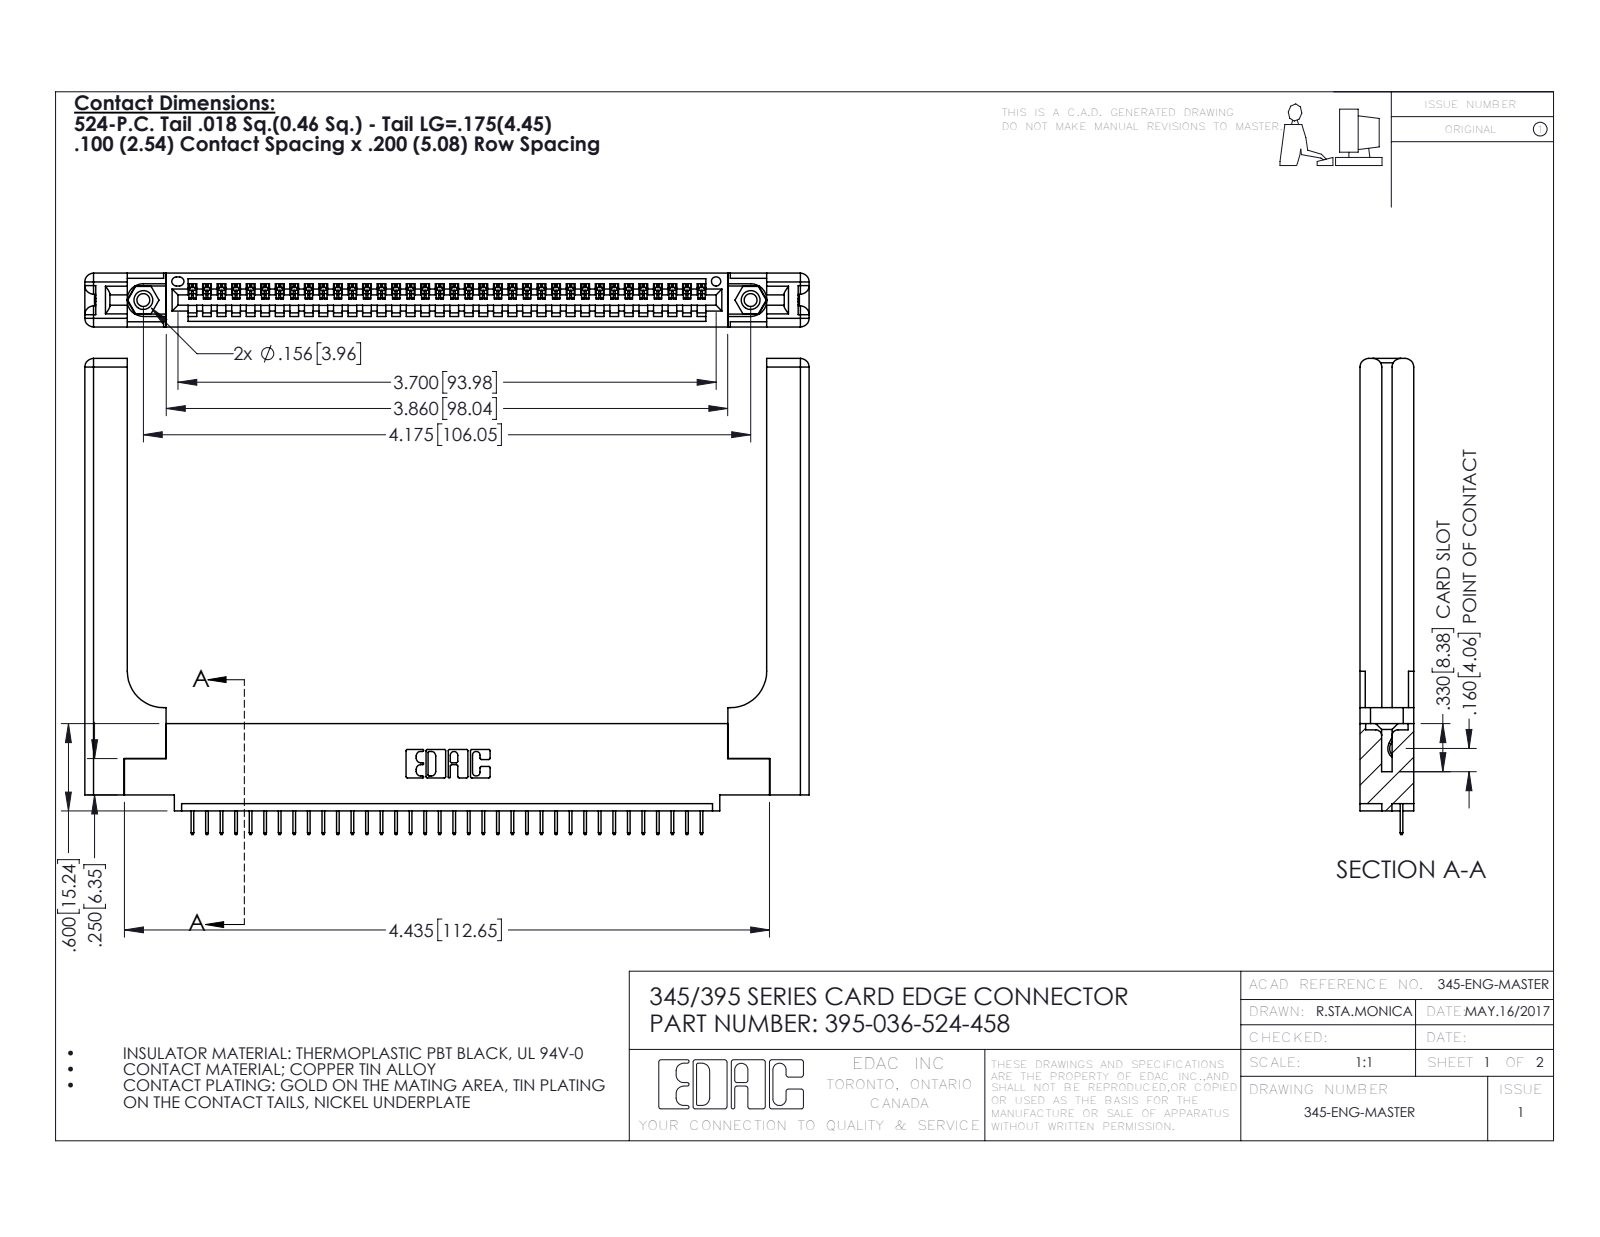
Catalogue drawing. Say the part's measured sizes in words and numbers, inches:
The part is named "395-036-524-458; 345-250-001_345-250-001-102; 345-220-058_345-220-058; 345-292-001_345-293-124 (+1 more)". Its 3-D file was written by "SolidWorks 2016 (CONFIG_CONTROL_DESIGN)". It is 41 solids with 2618 faces: 1888 planar, 670 cylindrical and 60 other. Overall it measures 4.979 by 3.272 by 0.37 inches. Its volume is 1.236 cubic inches and its surface area 31.72 square inches. Round holes: 2 of diameter 0.089, 2 of diameter 0.125, 2 of diameter 0.156, 1 of diameter 0.064. Round bosses or shafts: 2 of diameter 0.155. Partial cylindrical surfaces (rounded edges, fillets, slot ends): 72 of radius 0.006, 22 of radius 0.01, 16 of radius 0.06, 6 of radius 0.007, 6 of radius 0.031, 3 of radius 0.026, 2 of radius 0.03, 2 of radius 0.031. The main face-to-face distances are 0.37, 0.072, 0.298, 0.2, 0.098, 0.272, 0.025, 0.148, 0.15, 0.225. The hole center spacings are 0.27, 3.939, 4.175.
